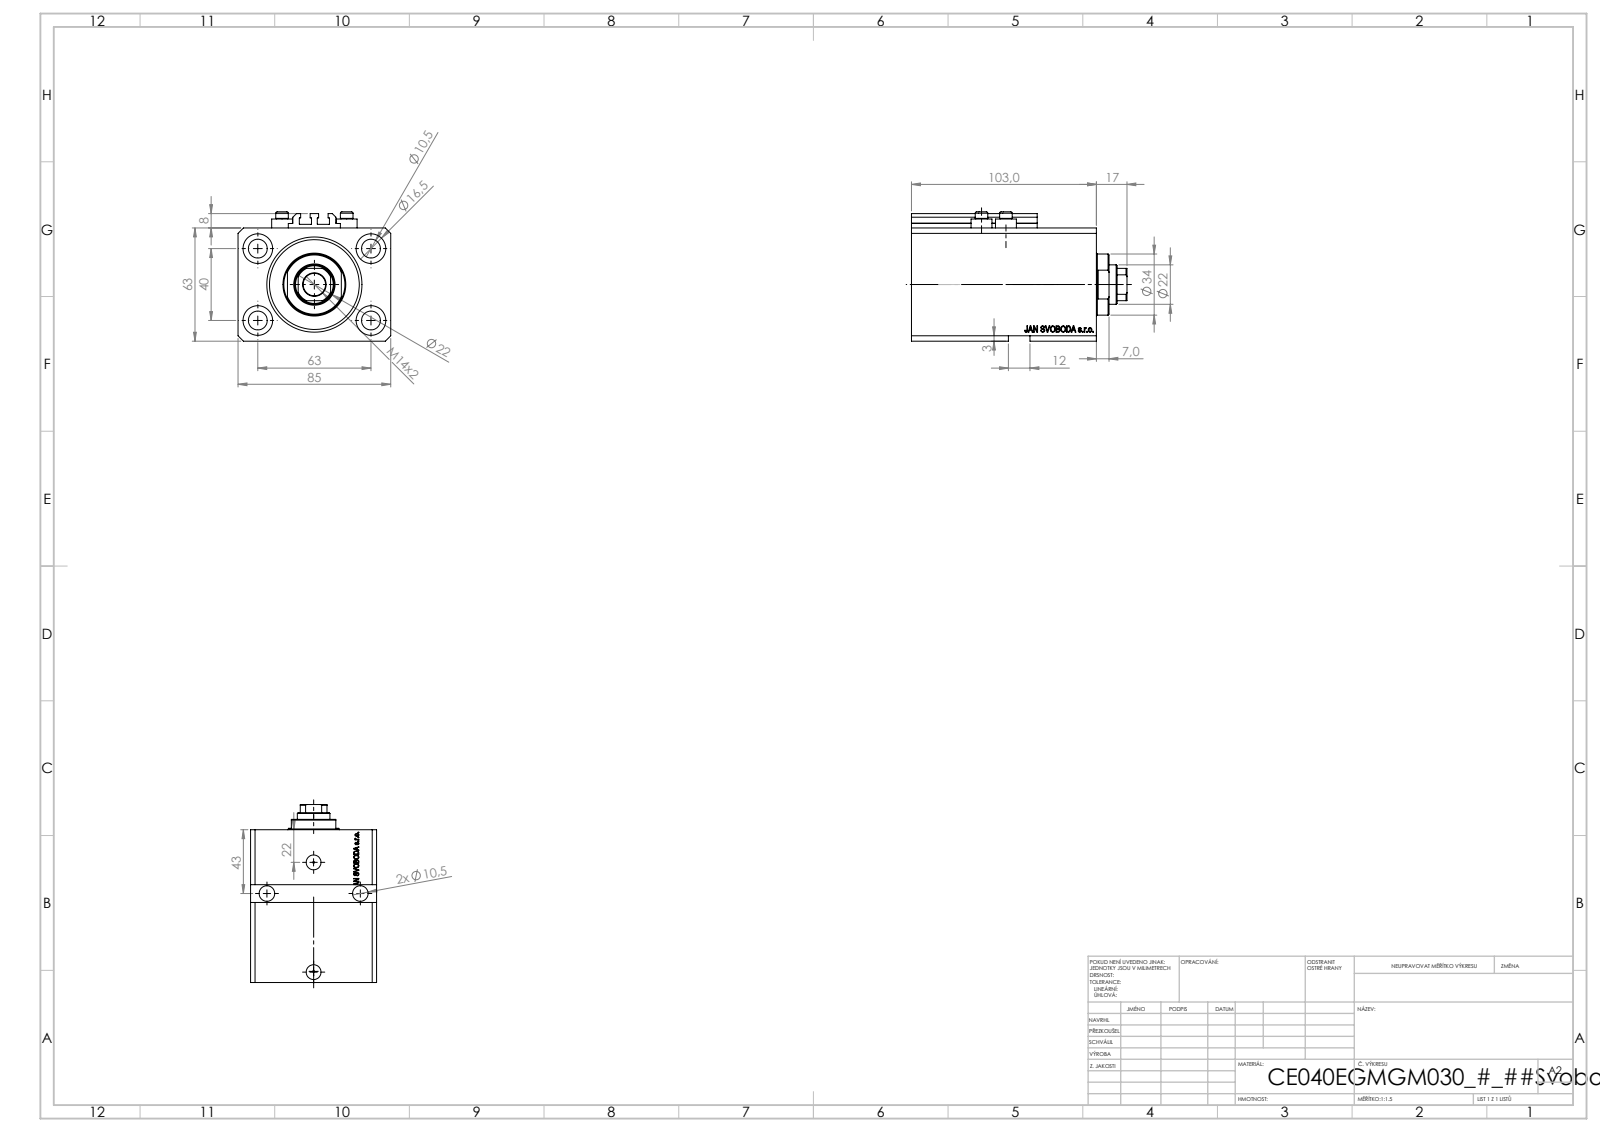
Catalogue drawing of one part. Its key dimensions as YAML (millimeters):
part_name: "ALLEN BOLT V250CE; V250CE_E_Body; V250CE_VC_E; V250CE_C_VCP"
step_written_by: "SolidWorks 2019 (CONFIG_CONTROL_DESIGN)"
units: millimeters
bodies: {solids: 8, faces: 1087, planar: 535, cylindrical: 126, other: 426}
overall_size: [120, 85, 72]
volume: 479656
surface_area: 102951
round_holes:
  - {diameter: 10.5, count: 6}
  - {diameter: 1.25, count: 4}
  - {diameter: 4, count: 4}
  - {diameter: 16.5, count: 4}
  - {diameter: 10, count: 2}
  - {diameter: 13.16, count: 2}
  - {diameter: 20, count: 2}
  - {diameter: 12.5, count: 1}
  - {diameter: 22, count: 1}
  - {diameter: 40, count: 1}
  - {diameter: 53, count: 1}
round_bosses_or_shafts:
  - {diameter: 11.6, count: 4}
  - {diameter: 7, count: 4}
  - {diameter: 34, count: 1}
partial_cylinders:
  - {radius: 0.2, count: 10}
  - {radius: 10.5, count: 1}
face_to_face_distances: [63, 85, 103, 17, 86, 11.4, 74.6, 91.6, 3, 65]
hole_center_spacings: [37.31, 63, 13.6, 15.4, 24.96, 33.62, 36, 36.25]
